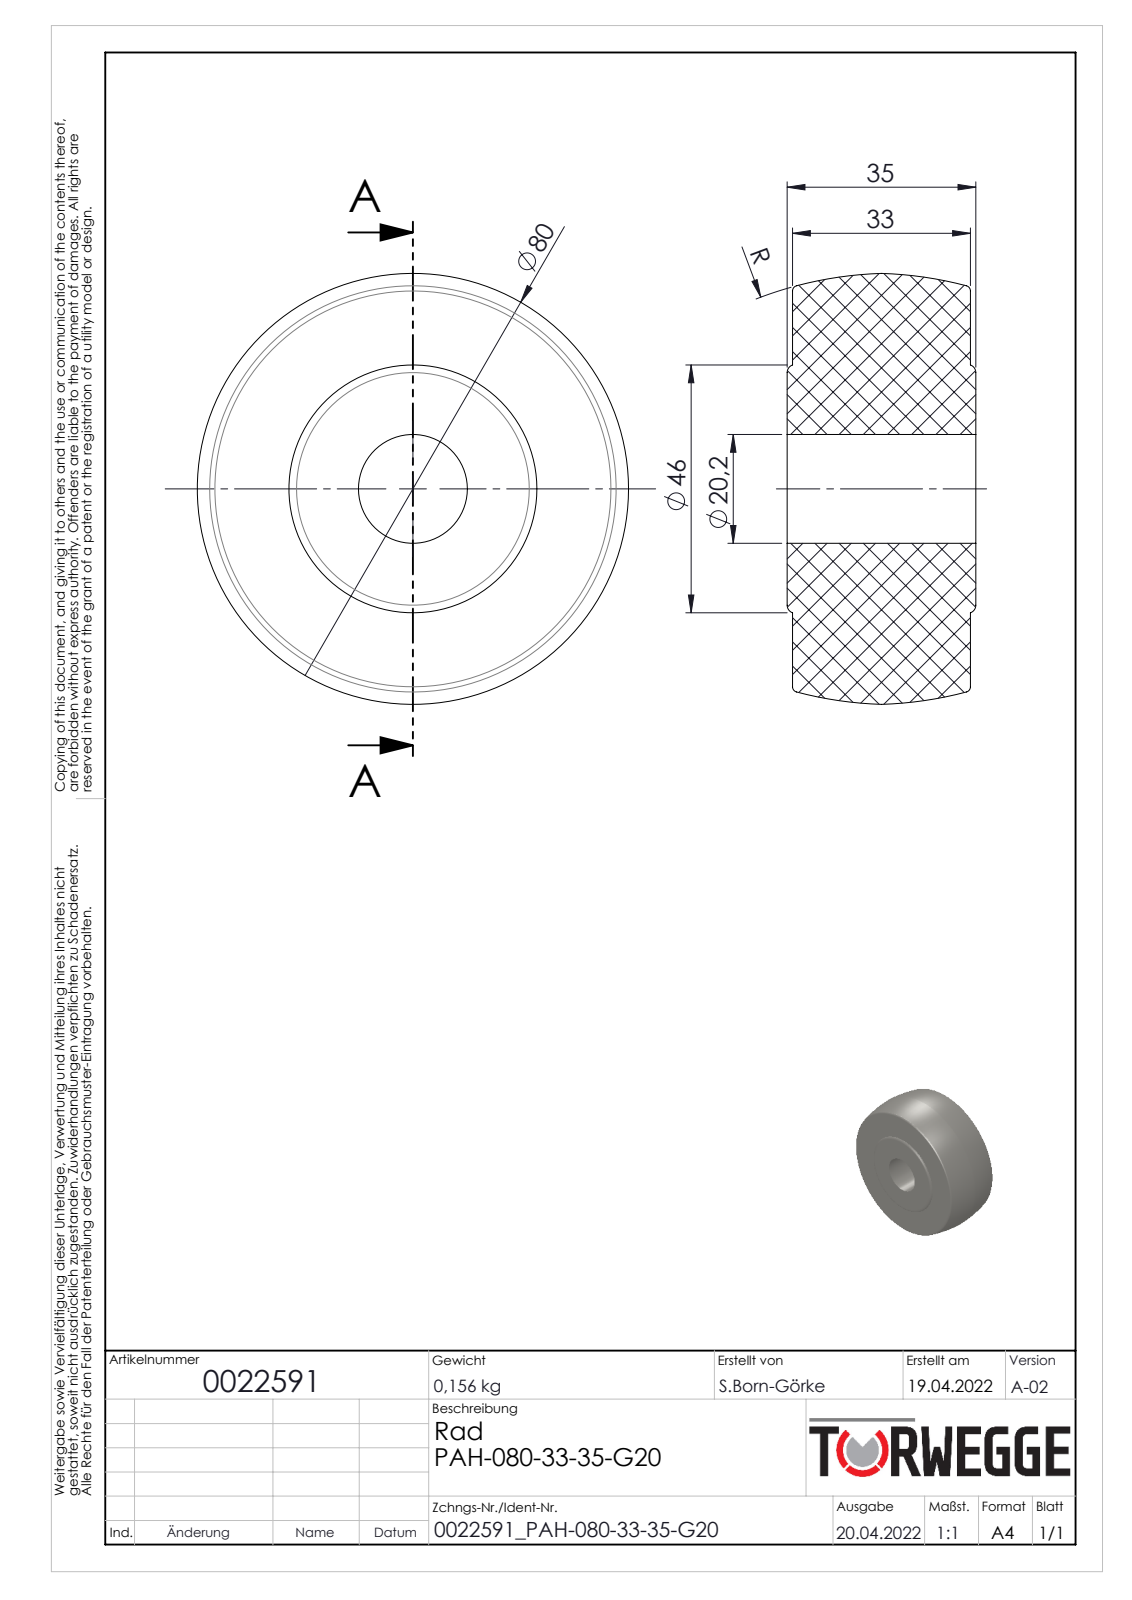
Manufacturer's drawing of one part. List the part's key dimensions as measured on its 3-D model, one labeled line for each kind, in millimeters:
Part name (STEP PRODUCT): 0022591
STEP written by: SolidWorks 2020 (AUTOMOTIVE_DESIGN)
Units: millimetres
Bodies: 1 solid, 18 faces (4 planar, 2 cylindrical, 12 other)
Overall size (bounding box): 80 × 80 × 35
Volume: 150 390 mm³ · Surface area: 18 648 mm²
Round holes (diameter × count): ⌀20.2 ×1
Main face-to-face distances: 33, 1, 34, 35
